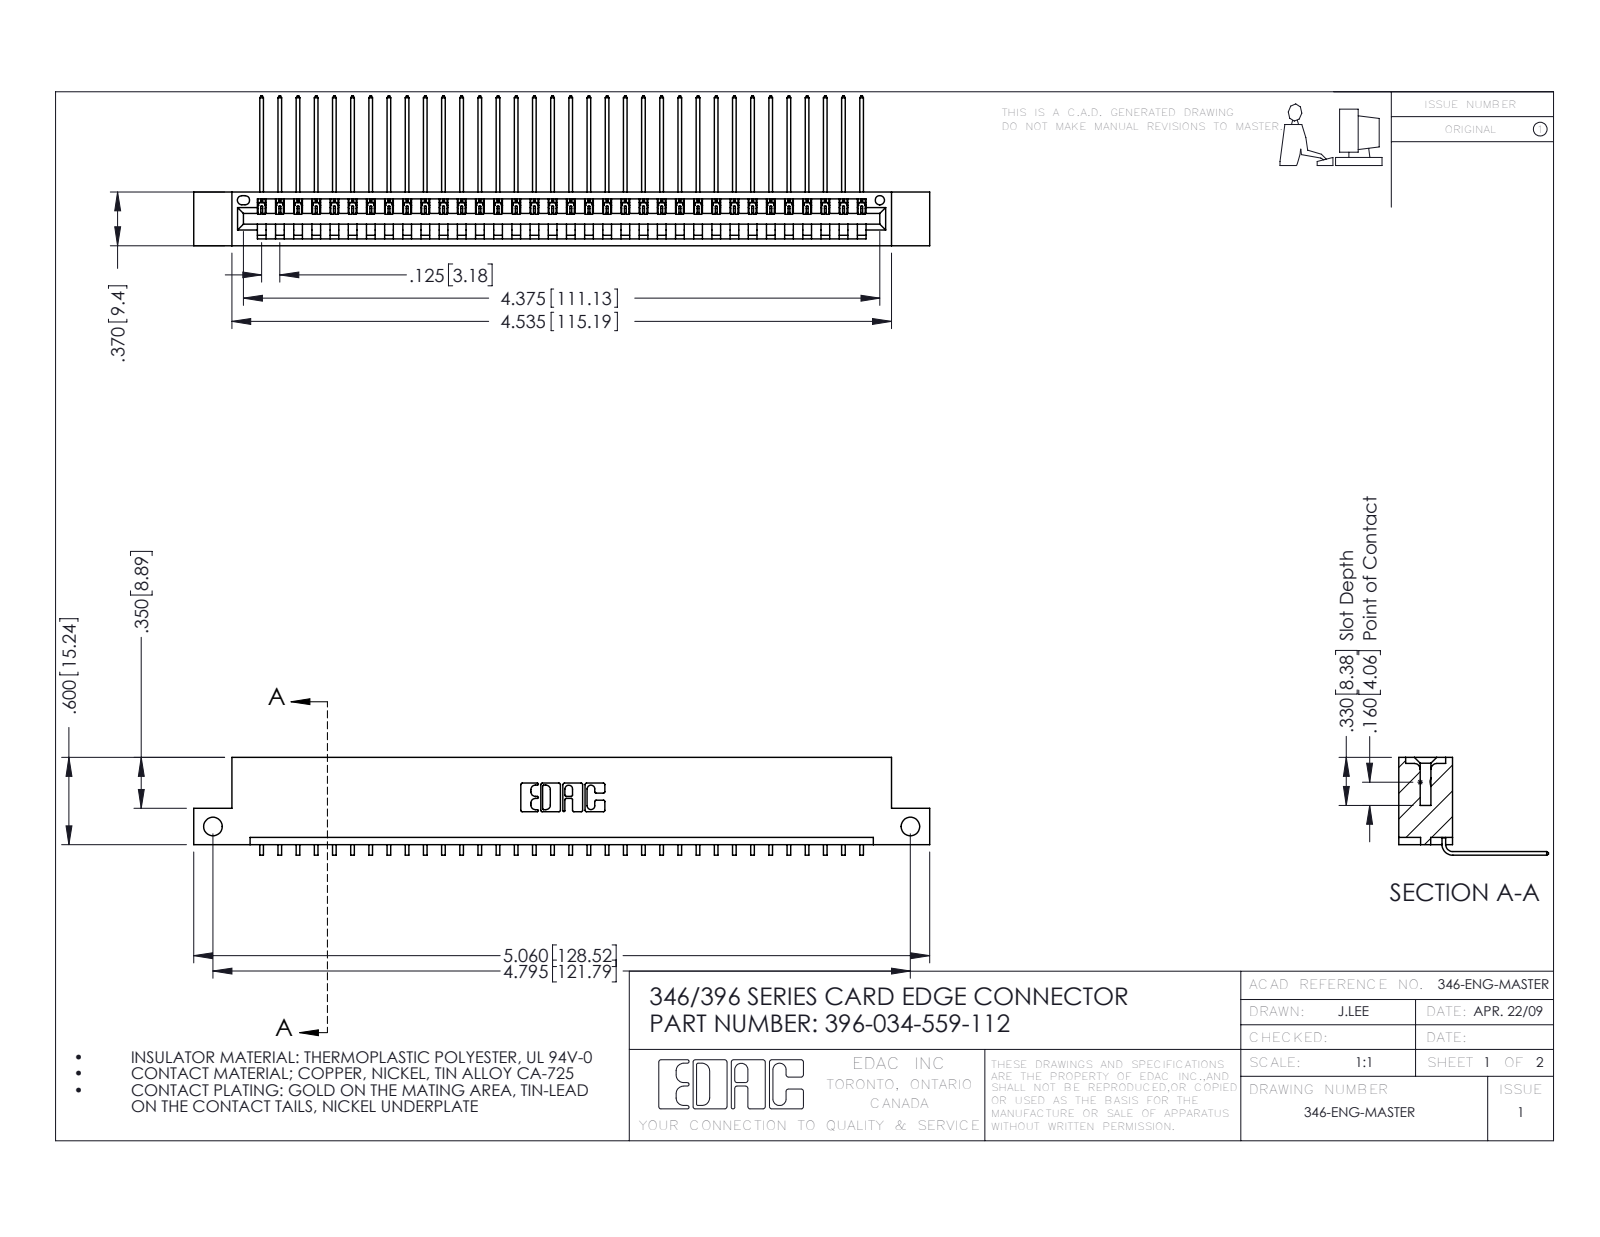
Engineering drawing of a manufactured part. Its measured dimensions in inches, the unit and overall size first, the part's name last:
Units: inches
Overall size (bounding box): 5.06 × 1.03 × 0.673
Round holes (diameter × count): ⌀0.128 ×2, ⌀0.064 ×1
Partial cylindrical surfaces — rounded edges, fillets, slot ends (radius × count): R0.006 ×68, R0.01 ×22, R0.007 ×6, R0.031 ×6, R0.026 ×3, R0.031 ×2, R0.04 ×2, R0.014 ×1
Main face-to-face distances: 0.048, 0.322, 0.37, 0.25, 0.072, 0.025, 0.298, 0.148, 0.222, 0.1
Hole centre spacings: 4.795
Volume: 0.749 in³ · Surface area: 24.47 in²
Bodies: 35 solids, 2162 faces (1504 planar, 658 cylindrical, 0 other)
Part name (STEP PRODUCT): 346 Part_Flush Mounting Lugs - Side Mount; 345-292-001_558 559 Tail - 1; 396-034-559-112
STEP written by: SolidWorks 2016 (CONFIG_CONTROL_DESIGN)
